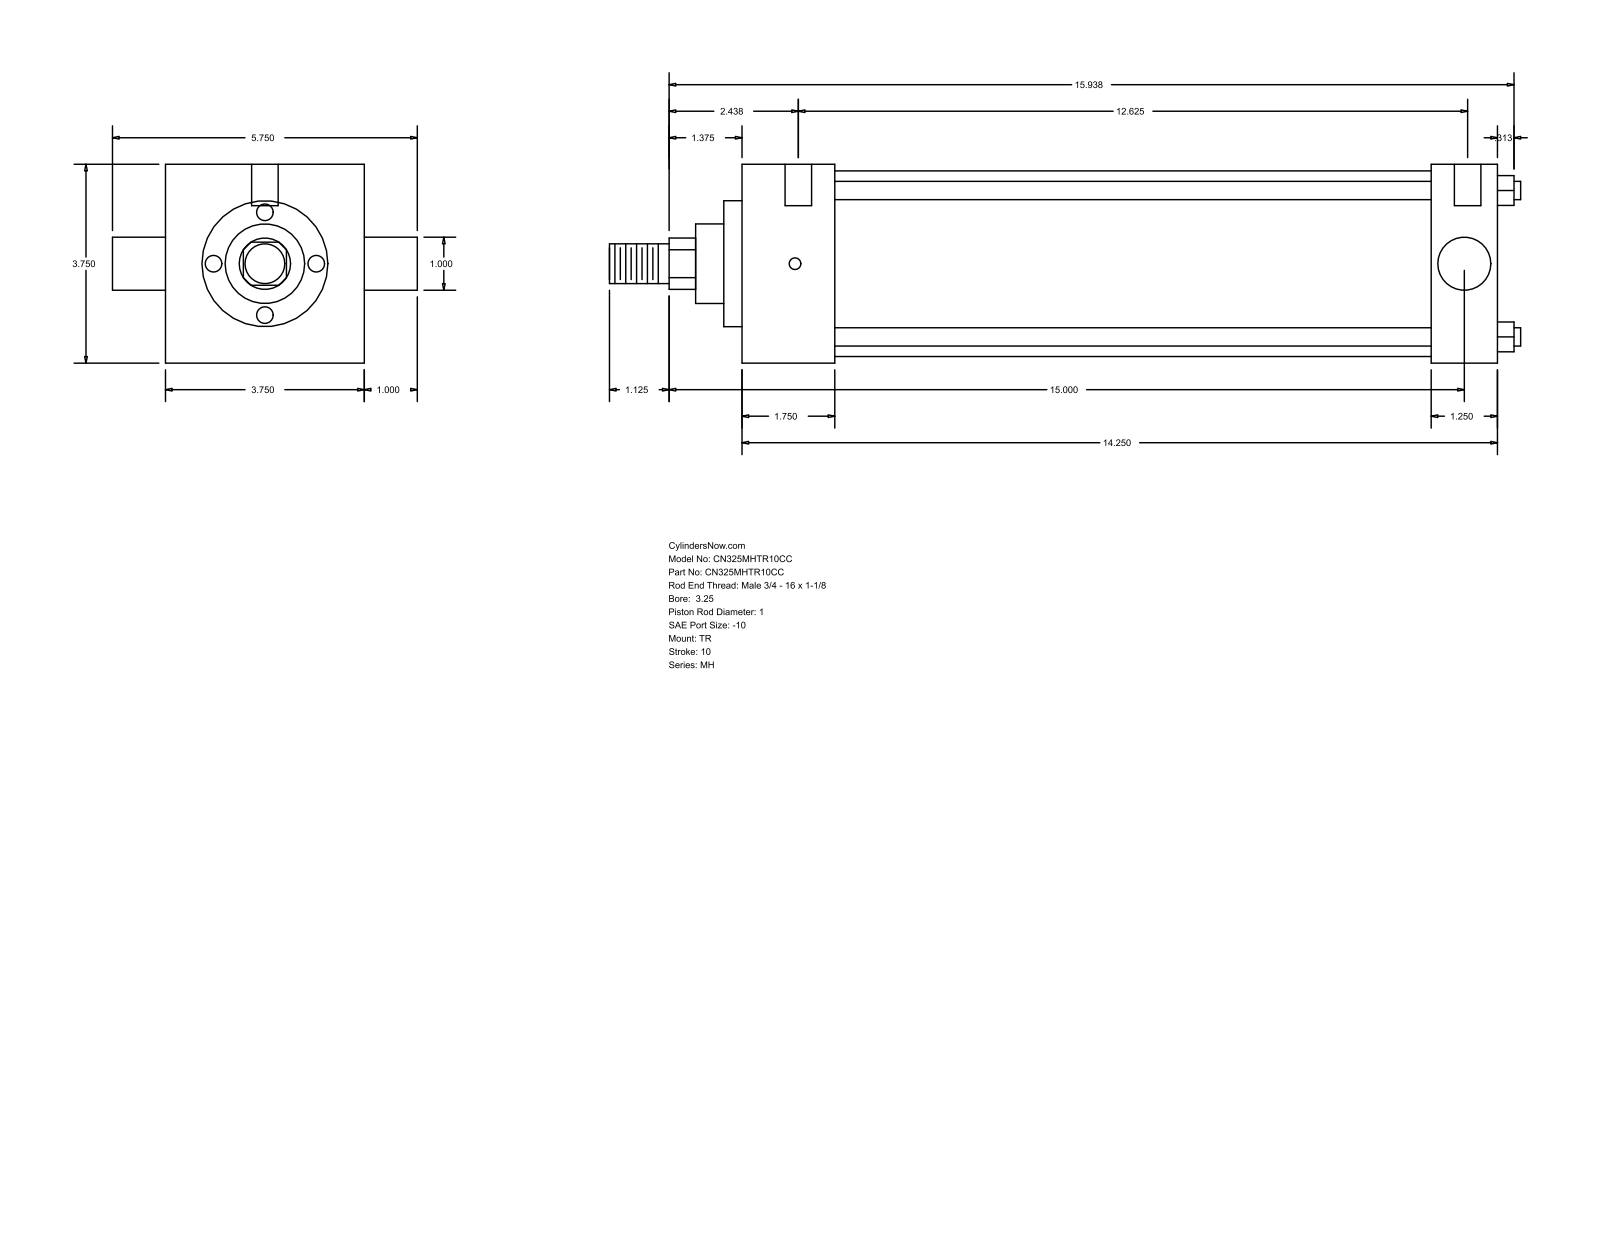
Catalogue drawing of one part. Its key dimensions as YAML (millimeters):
part_name: "MH_TR__0325_1"
step_written_by: "GSSL Pune (CONFIG_CONTROL_DESIGN)"
units: millimeters
bodies: {solids: 0, faces: 86, planar: 61, cylindrical: 25, other: 0}
overall_size: [436.56, 146.05, 95.25]
round_holes:
  - {diameter: 5.56, count: 3}
  - {diameter: 12.7, count: 2}
round_bosses_or_shafts:
  - {diameter: 8.76, count: 4}
  - {diameter: 25.4, count: 2}
  - {diameter: 88.9, count: 1}
  - {diameter: 60.33, count: 1}
  - {diameter: 38.1, count: 1}
  - {diameter: 19.05, count: 1}
partial_cylinders:
  - {radius: 12.29, count: 1}
face_to_face_distances: [95.24, 361.96, 44.46, 330.2, 285.74, 317.5, 31.76, 8.73, 53.19, 338.93]
hole_center_spacings: [1.58, 4.76, 320.68, 322.26, 325.44, 327.02]
